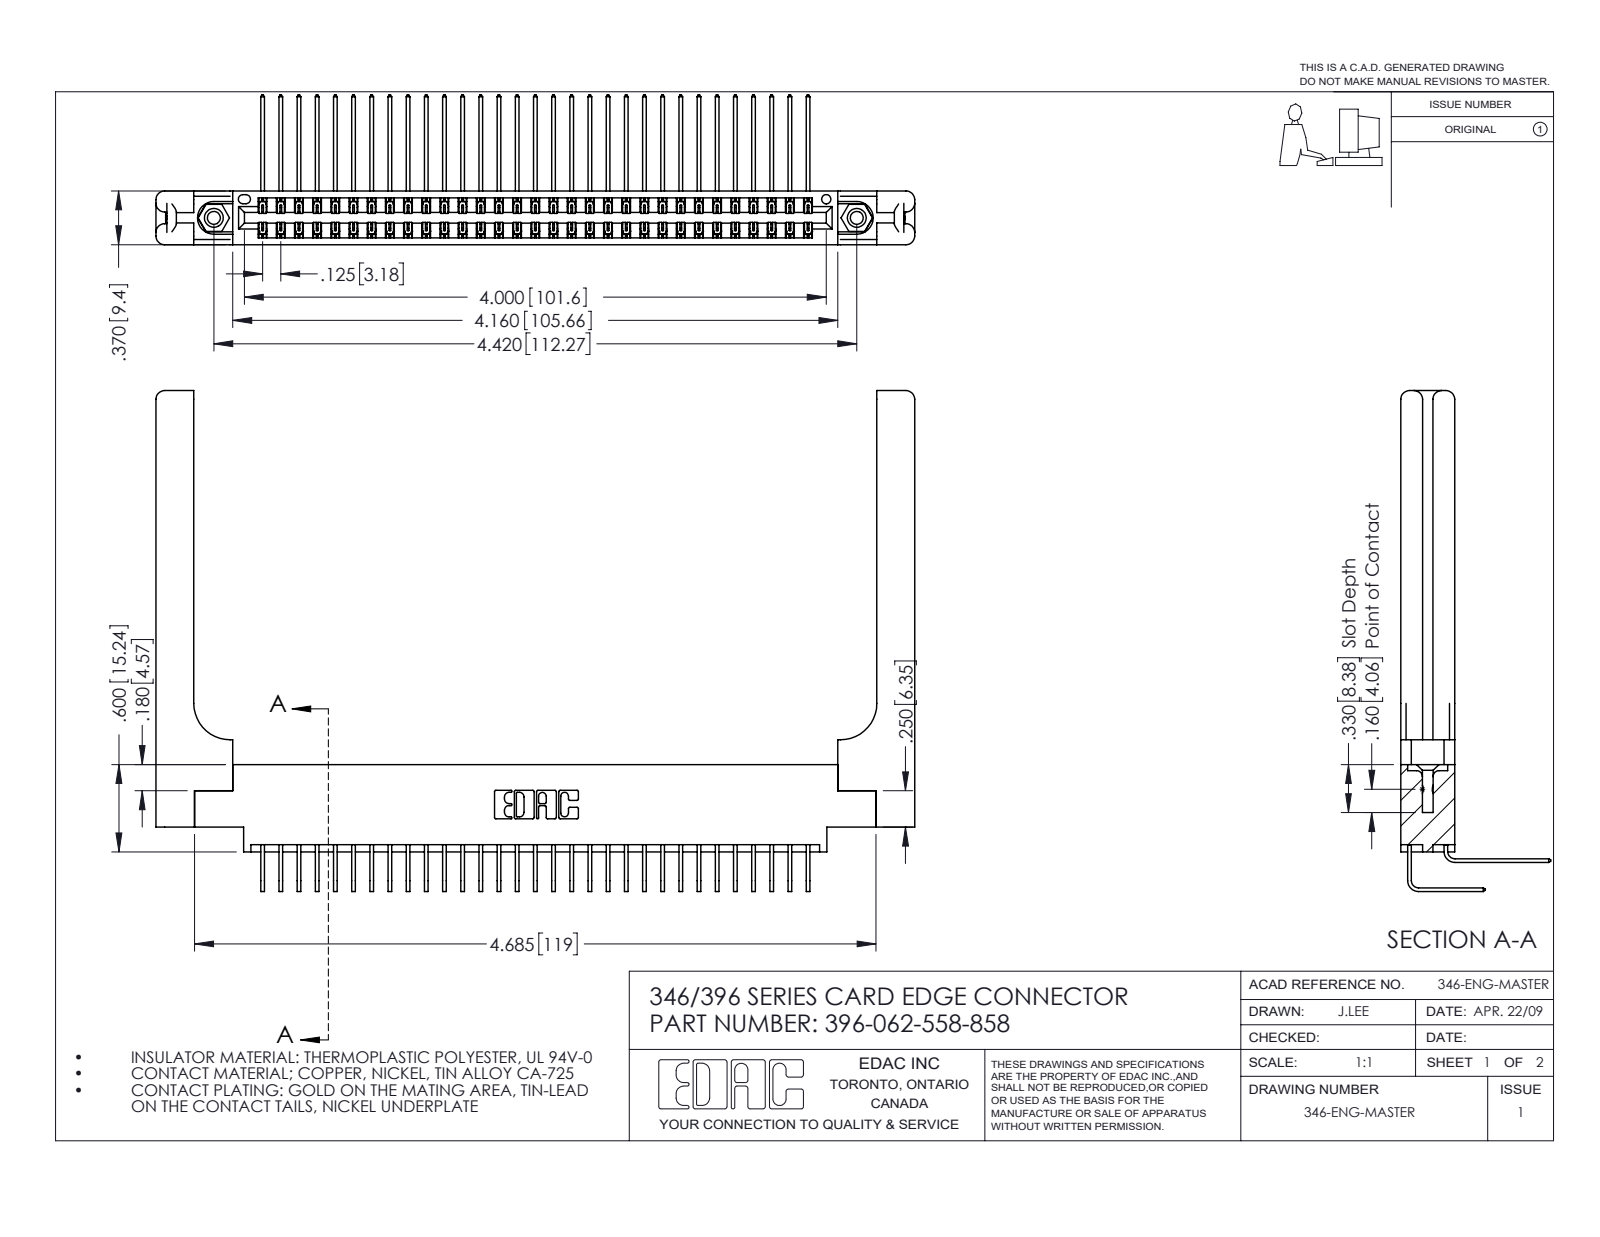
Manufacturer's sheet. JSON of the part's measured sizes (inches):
{"part_name": "346 Part_0.170 Offset - 0.156 Dia-TH; 396-062-558-858; 346-220-058_345-220-058; 345-292-001_558 Tail - 2 (+2 more)", "step_written_by": "SolidWorks 2016 (CONFIG_CONTROL_DESIGN)", "units": "inches", "bodies": {"solids": 67, "faces": 3730, "planar": 2522, "cylindrical": 1148, "other": 60}, "overall_size": [5.216, 3.443, 1.03], "volume_in3": 1.253, "surface_area_in2": 38.15, "round_holes": [[0.089, 2], [0.125, 2], [0.156, 2], [0.064, 1]], "round_bosses_or_shafts": [[0.155, 2]], "partial_cylinders_radius": [[0.006, 93], [0.01, 22], [0.06, 16], [0.007, 6], [0.031, 6], [0.026, 3], [0.014, 2], [0.022, 2]], "face_to_face_distances": [0.37, 0.322, 0.048, 0.072, 0.025, 0.148, 0.15, 0.298, 0.25, 0.275], "hole_center_spacings": [0.246, 4.212, 4.42]}
